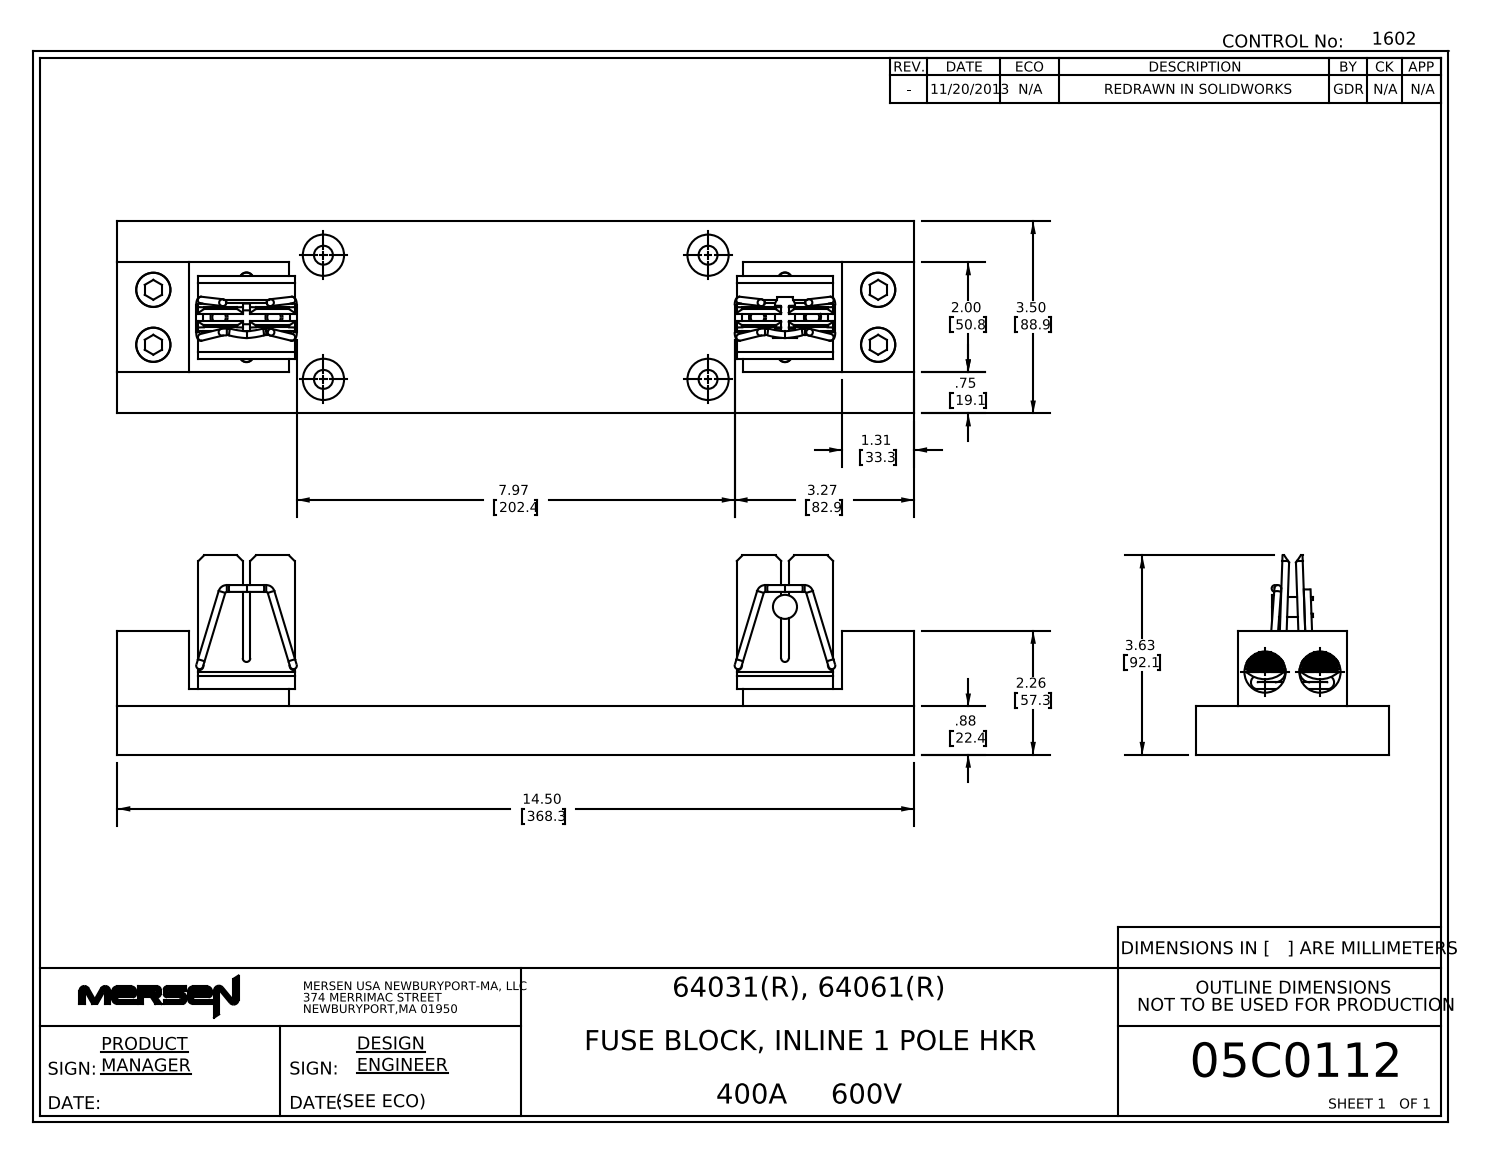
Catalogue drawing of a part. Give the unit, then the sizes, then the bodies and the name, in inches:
Units: inches
Overall size (bounding box): 14.504 × 3.627 × 3.5
Round holes (diameter × count): ⌀0.257 ×8, ⌀0.625 ×8, ⌀0.75 ×6, ⌀0.339 ×4, ⌀0.344 ×4, ⌀0.85 ×4, ⌀0.316 ×2, ⌀0.377 ×2
Round bosses / shafts (diameter × count): ⌀0.313 ×8, ⌀0.438 ×1, ⌀0.375 ×1
Partial cylindrical surfaces — rounded edges, fillets, slot ends (radius × count): R0.094 ×4, R0.125 ×3, R0.063 ×2, R0.069 ×2, R0.187 ×2, R0.141 ×1, R0.195 ×1
Main face-to-face distances: 0.88, 0.124, 3.5, 0.312, 1.192, 0.75, 2.75, 0.124, 0.25, 2.255
Hole centre spacings: 9.8, 0.851, 0.852, 8.411, 9.326, 11.498, 11.557, 1
Volume: 53.36 in³ · Surface area: 287.4 in²
Bodies: 20 solids, 521 faces (234 planar, 86 cylindrical, 201 other)
Part name (STEP PRODUCT): 05C0112rev
STEP written by: SolidWorks 2013 (AUTOMOTIVE_DESIGN)
